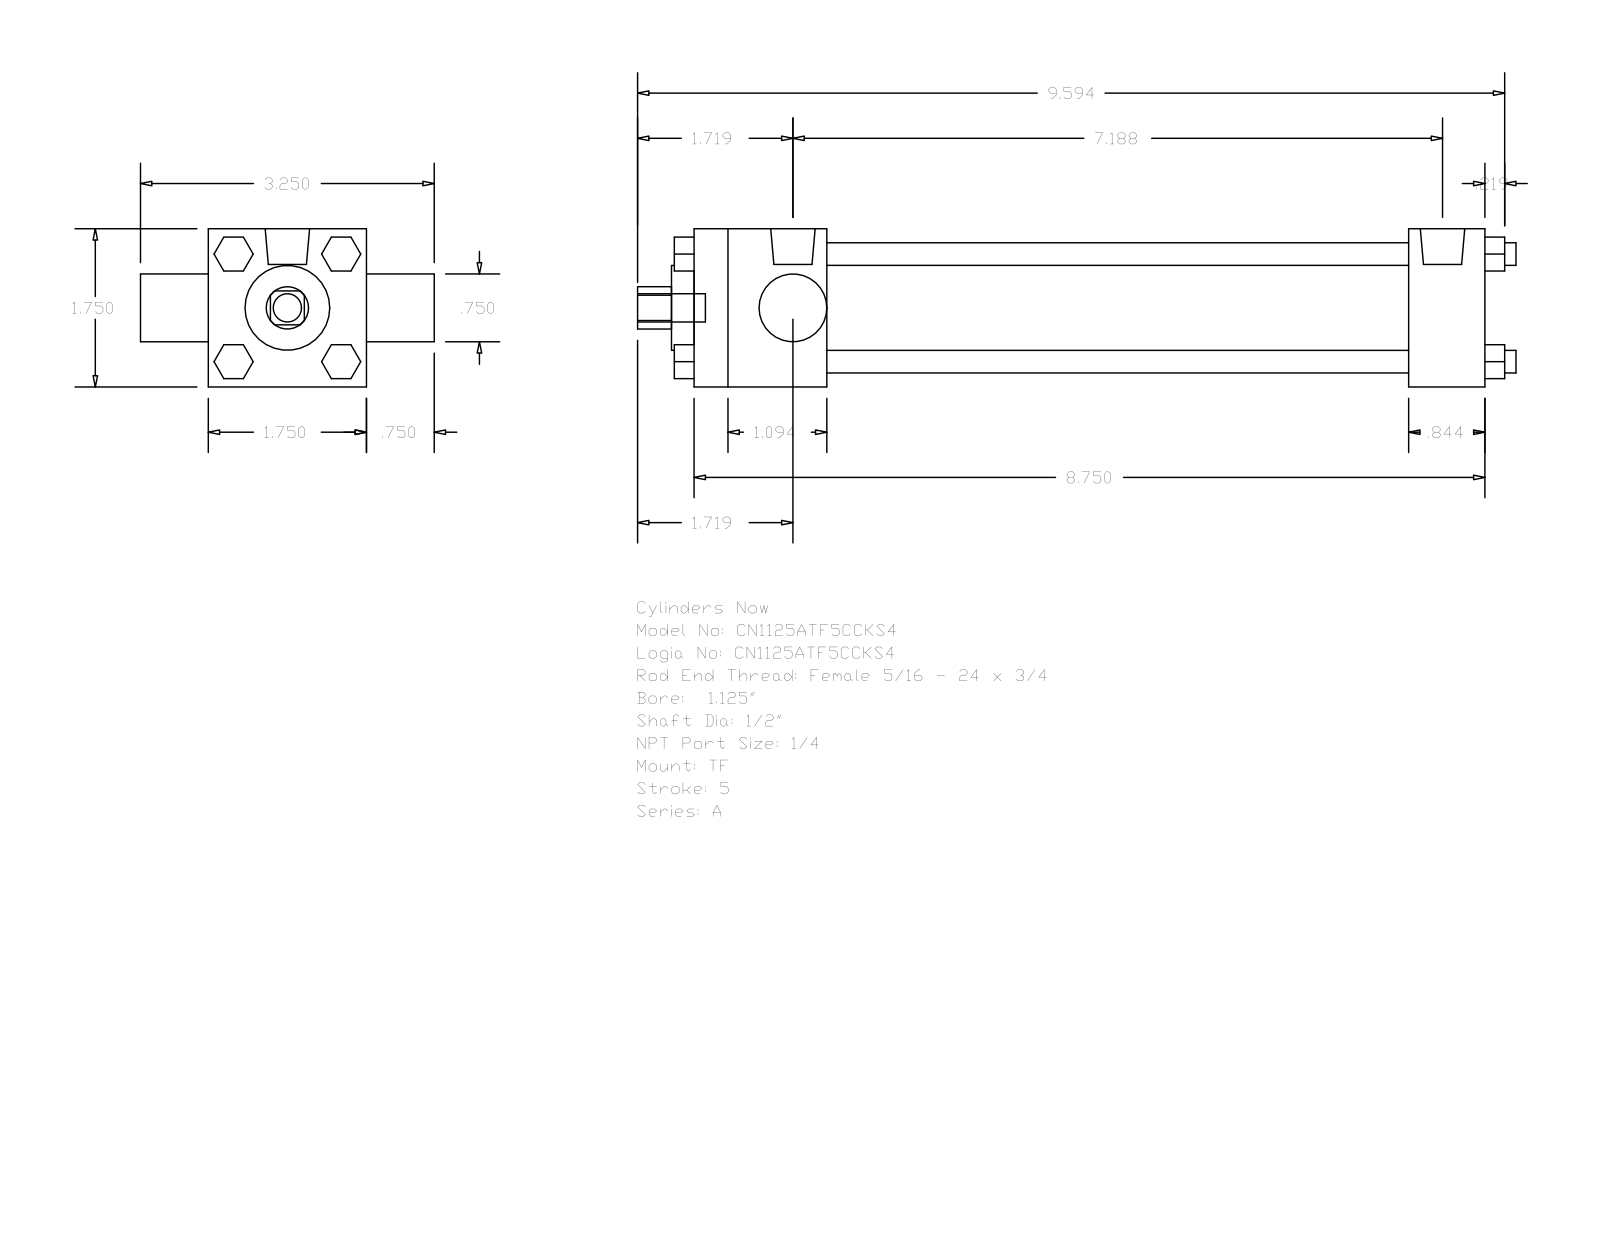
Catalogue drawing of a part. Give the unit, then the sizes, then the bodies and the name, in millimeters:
Units: millimetres
Overall size (bounding box): 246.86 × 82.55 × 44.45
Round holes (diameter × count): ⌀12.7 ×1, ⌀19.05 ×1, ⌀23.81 ×1, ⌀31.88 ×1
Round bosses / shafts (diameter × count): ⌀6.35 ×4, ⌀5.56 ×3, ⌀12.49 ×2, ⌀7.94 ×1
Partial cylindrical surfaces — rounded edges, fillets, slot ends (radius × count): R5.94 ×1
Main face-to-face distances: 44.46, 222.24, 200.81, 21.43, 37.3, 163.51, 184.94, 19.04, 63.5, 9.53
Bodies: 0 solids, 120 faces (92 planar, 28 cylindrical, 0 other)
Part name (STEP PRODUCT): A_TF__0112_0.5
STEP written by: GSSL Pune (CONFIG_CONTROL_DESIGN)
